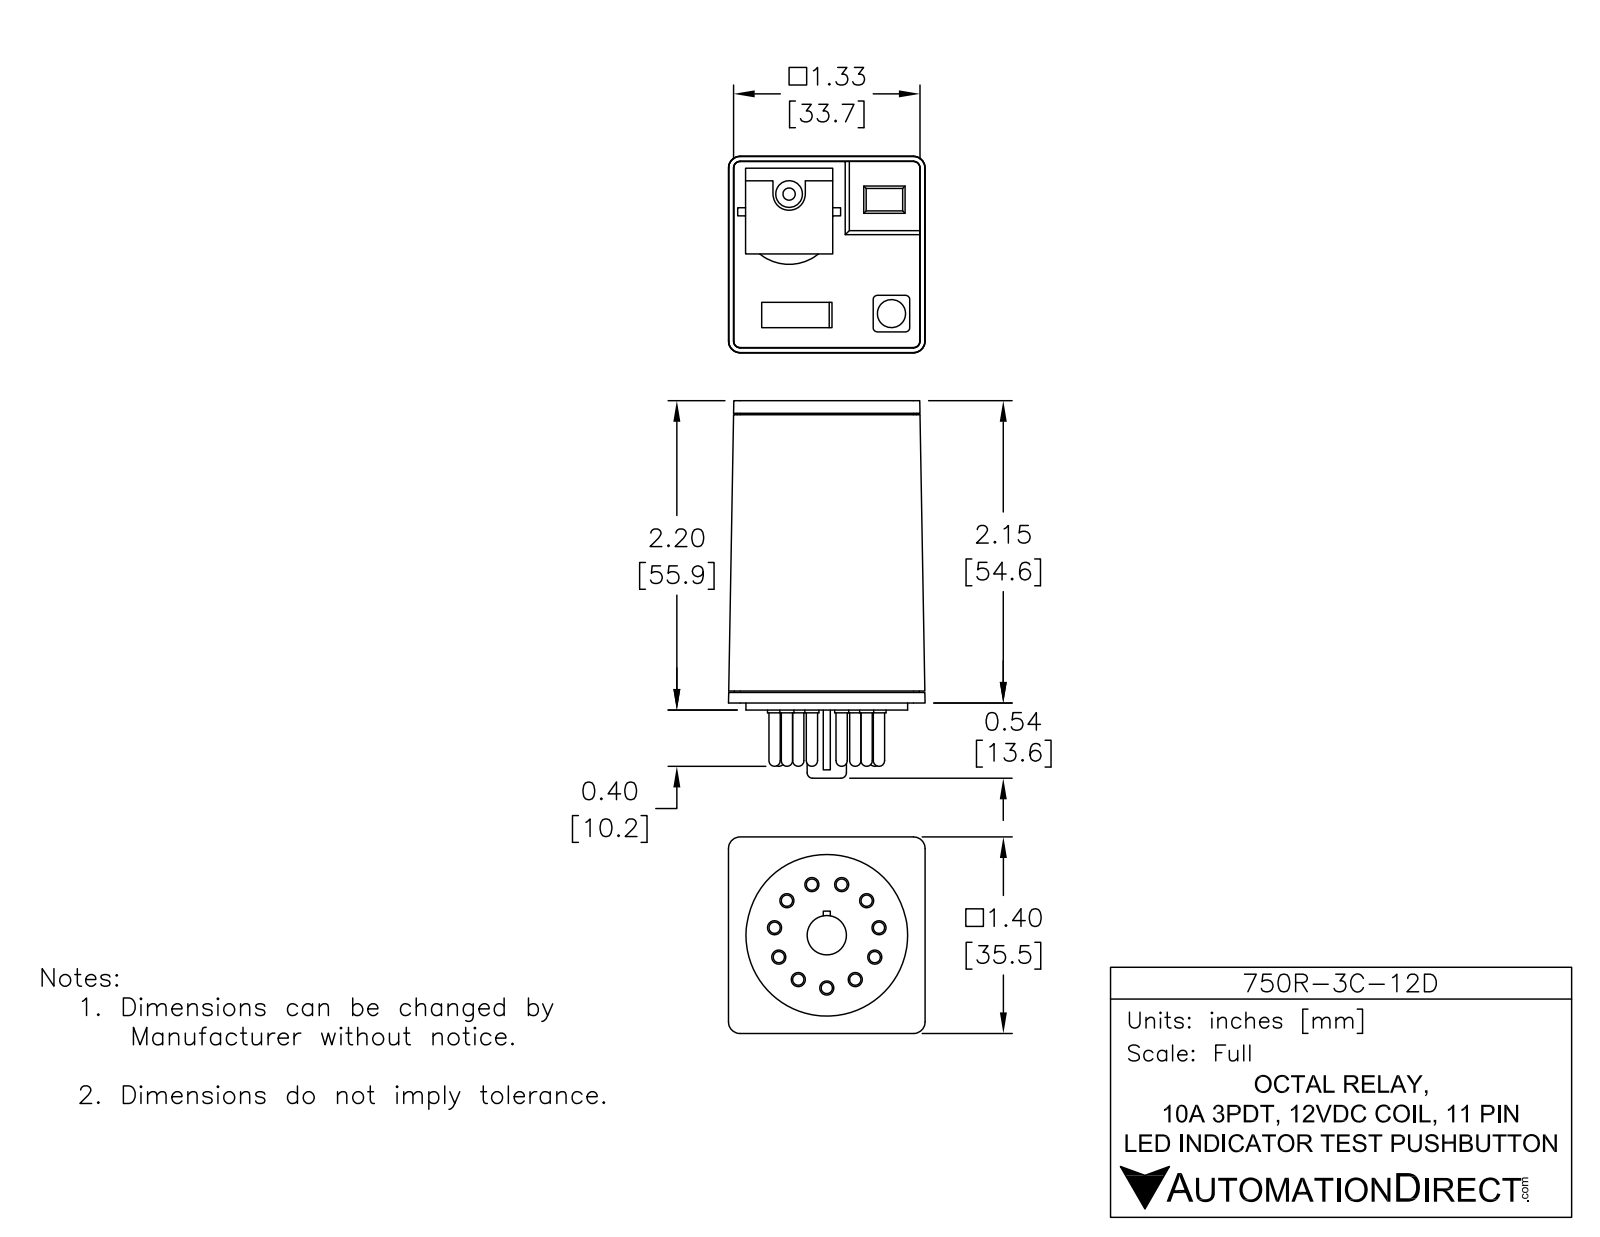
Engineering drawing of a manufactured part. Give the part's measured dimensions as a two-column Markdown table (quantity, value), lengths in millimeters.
| quantity | value |
| --- | --- |
| part name | 750R-3C-12D |
| STEP written by | SolidWorks 2014 (AUTOMOTIVE_DESIGN) |
| units | millimeters |
| bodies | 1 solid, 180 faces (93 planar, 62 cylindrical, 25 other) |
| overall size | 68.2 × 35.5 × 35.5 |
| volume | 66 470 mm³ |
| surface area | 11 410 mm² |
| round holes (diameter × count) | 2.2 × 1, 5.1 × 1 |
| round bosses / shafts (diameter × count) | 2.5 × 11, 2 × 11, 29.2 × 1, 7.1 × 1, 4.8 × 1 |
| partial cylindrical surfaces (radius × count) | 0.8 × 4, 2.9 × 1, 8.4 × 1 |
| main face-to-face distances | 1.3, 54.6, 55.9, 53.6, 1, 55.6, 54.4, 2.2, 0.8, 54.9 |
| hole center spacings | 28.4 |
